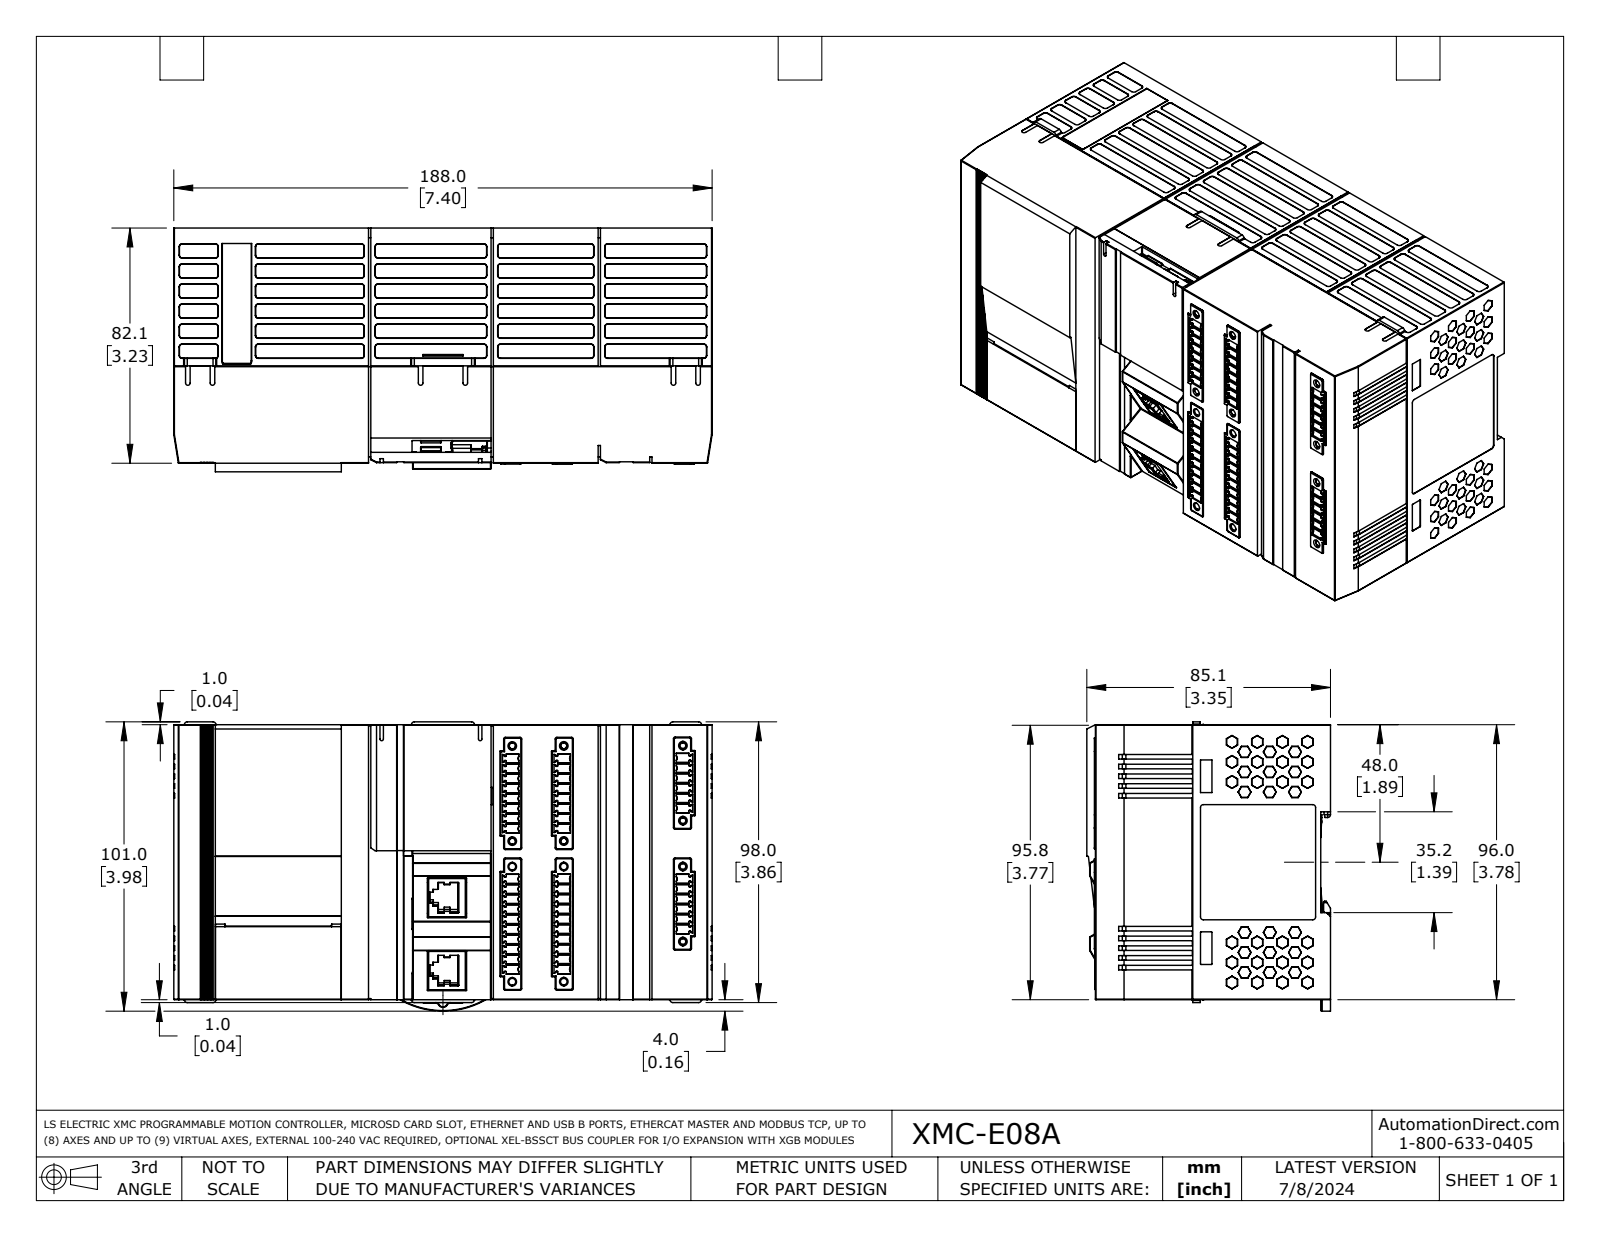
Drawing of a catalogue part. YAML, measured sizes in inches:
part_name: "XMC-E08A"
step_written_by: "SolidWorks 2021 (AUTOMOTIVE_DESIGN)"
units: inches
bodies: {solids: 1, faces: 4920, planar: 3175, cylindrical: 1089, other: 656}
overall_size: [7.402, 3.976, 3.35]
volume: 87.08
surface_area: 157
round_holes:
  - {diameter: 0.079, count: 4}
  - {diameter: 0.083, count: 1}
  - {diameter: 0.098, count: 1}
  - {diameter: 0.134, count: 1}
round_bosses_or_shafts:
  - {diameter: 0.209, count: 5}
  - {diameter: 0.118, count: 5}
  - {diameter: 0.079, count: 4}
  - {diameter: 0.205, count: 1}
  - {diameter: 0.157, count: 1}
partial_cylinders:
  - {radius: 0.008, count: 448}
  - {radius: 0.02, count: 144}
  - {radius: 0.039, count: 87}
  - {radius: 0.012, count: 46}
  - {radius: 0.062, count: 40}
  - {radius: 0.024, count: 27}
  - {radius: 0.01, count: 12}
  - {radius: 0.031, count: 7}
face_to_face_distances: [3.777, 3.78, 3.098, 3.775, 7.398, 3.232, 7.402, 0.134, 3.091, 3.224]
hole_center_spacings: [0.465, 0.631, 1.031, 1.031, 1.106, 1.661, 1.662, 1.699]
